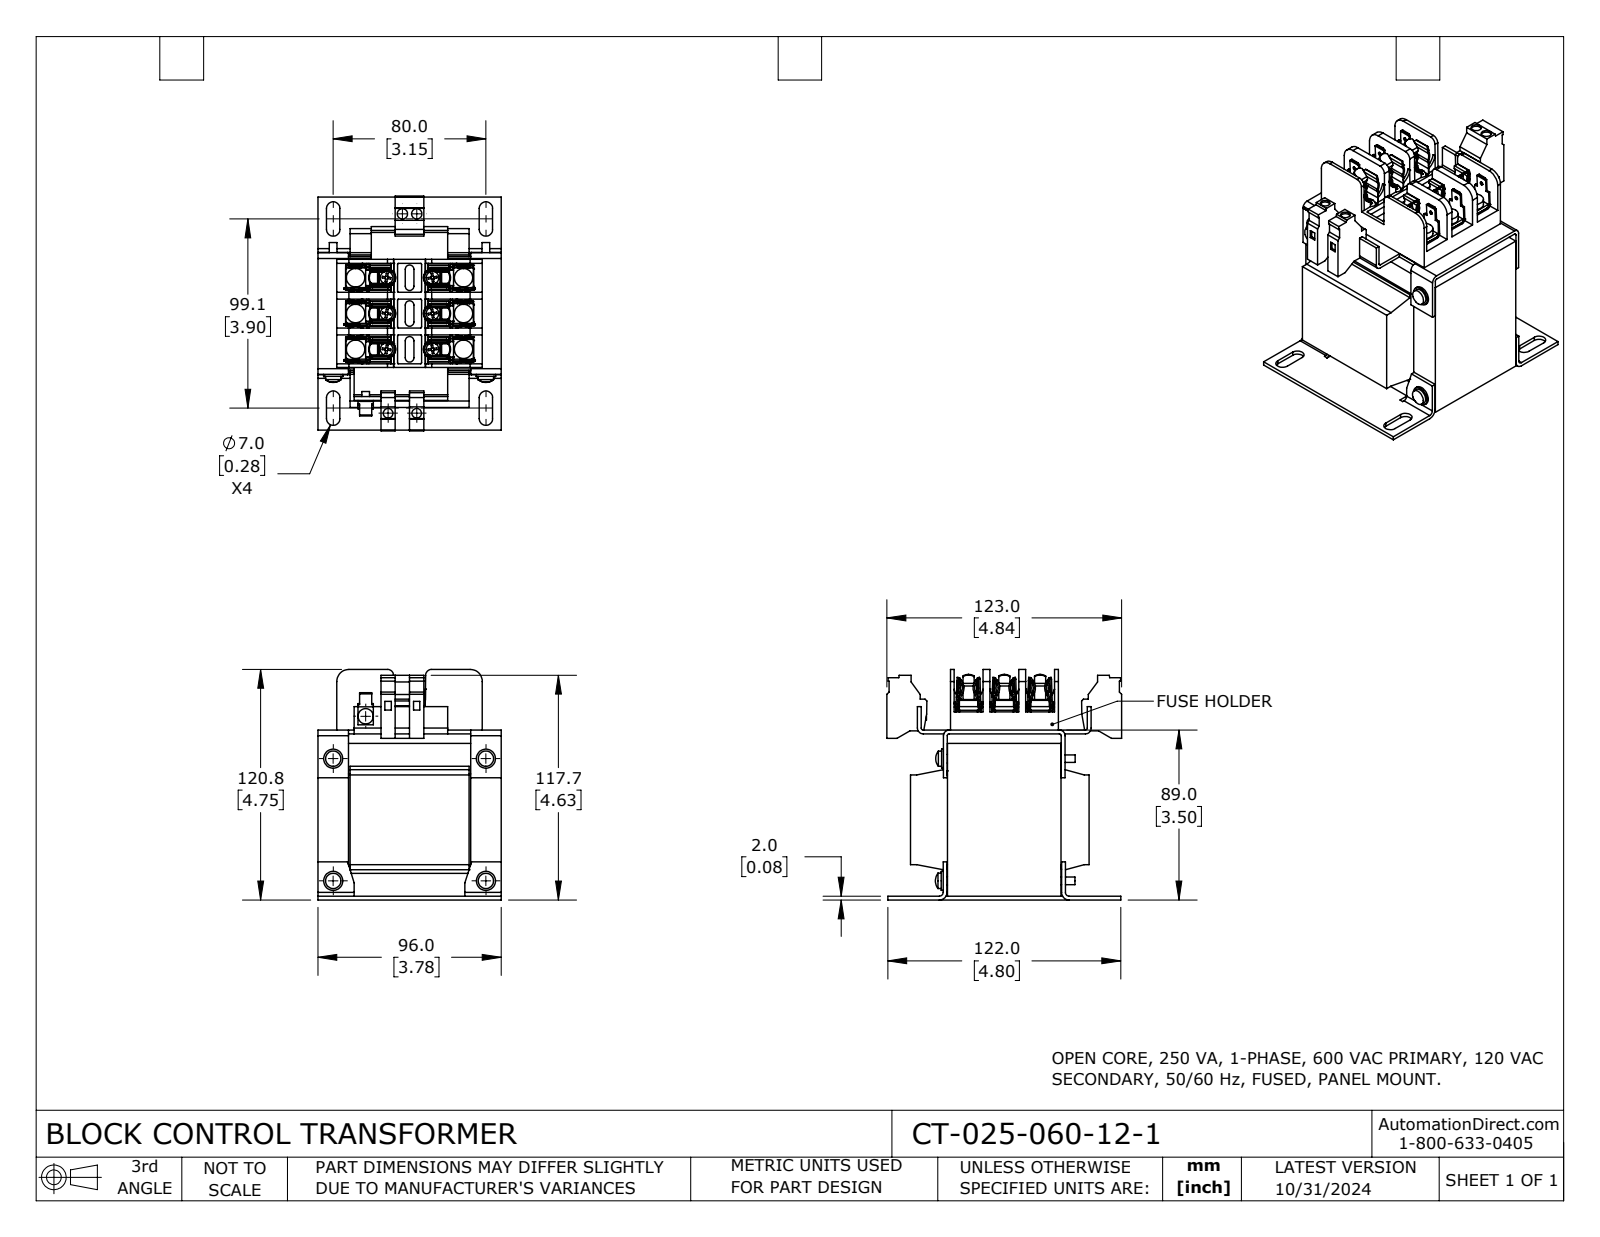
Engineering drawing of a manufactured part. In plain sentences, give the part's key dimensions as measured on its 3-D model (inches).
The part is named "CT-025-060-12-1". Its 3-D file was written by "SolidWorks 2023 (CONFIG_CONTROL_DESIGN)". It is 2 solids with 1591 faces: 1033 planar, 524 cylindrical and 34 other. Overall it measures 4.843 by 4.754 by 3.78 inches. Its volume is 41.28 cubic inches and its surface area 222.7 square inches. Round holes: 12 of diameter 0.074, 5 of diameter 0.205, 2 of diameter 0.197, 2 of diameter 0.213, 1 of diameter 0.205. Round bosses or shafts: 6 of diameter 0.38, 6 of diameter 0.19, 5 of diameter 0.315, 5 of diameter 0.157, 4 of diameter 0.394, 4 of diameter 0.177. Partial cylindrical surfaces (rounded edges, fillets, slot ends): 24 of radius 0.01, 20 of radius 0.05, 18 of radius 0.03, 14 of radius 0.072, 12 of radius 0.038, 12 of radius 0.04, 12 of radius 0.164, 9 of radius 0.097. The main face-to-face distances are 0.079, 3.425, 3.15, 0.63, 0.661, 3.118, 3.504, 2.52, 3.346, 0.197. The hole center spacings are 2.232, 2.354, 0.026, 0.026, 0.052, 0.738, 2.345, 1.633.
